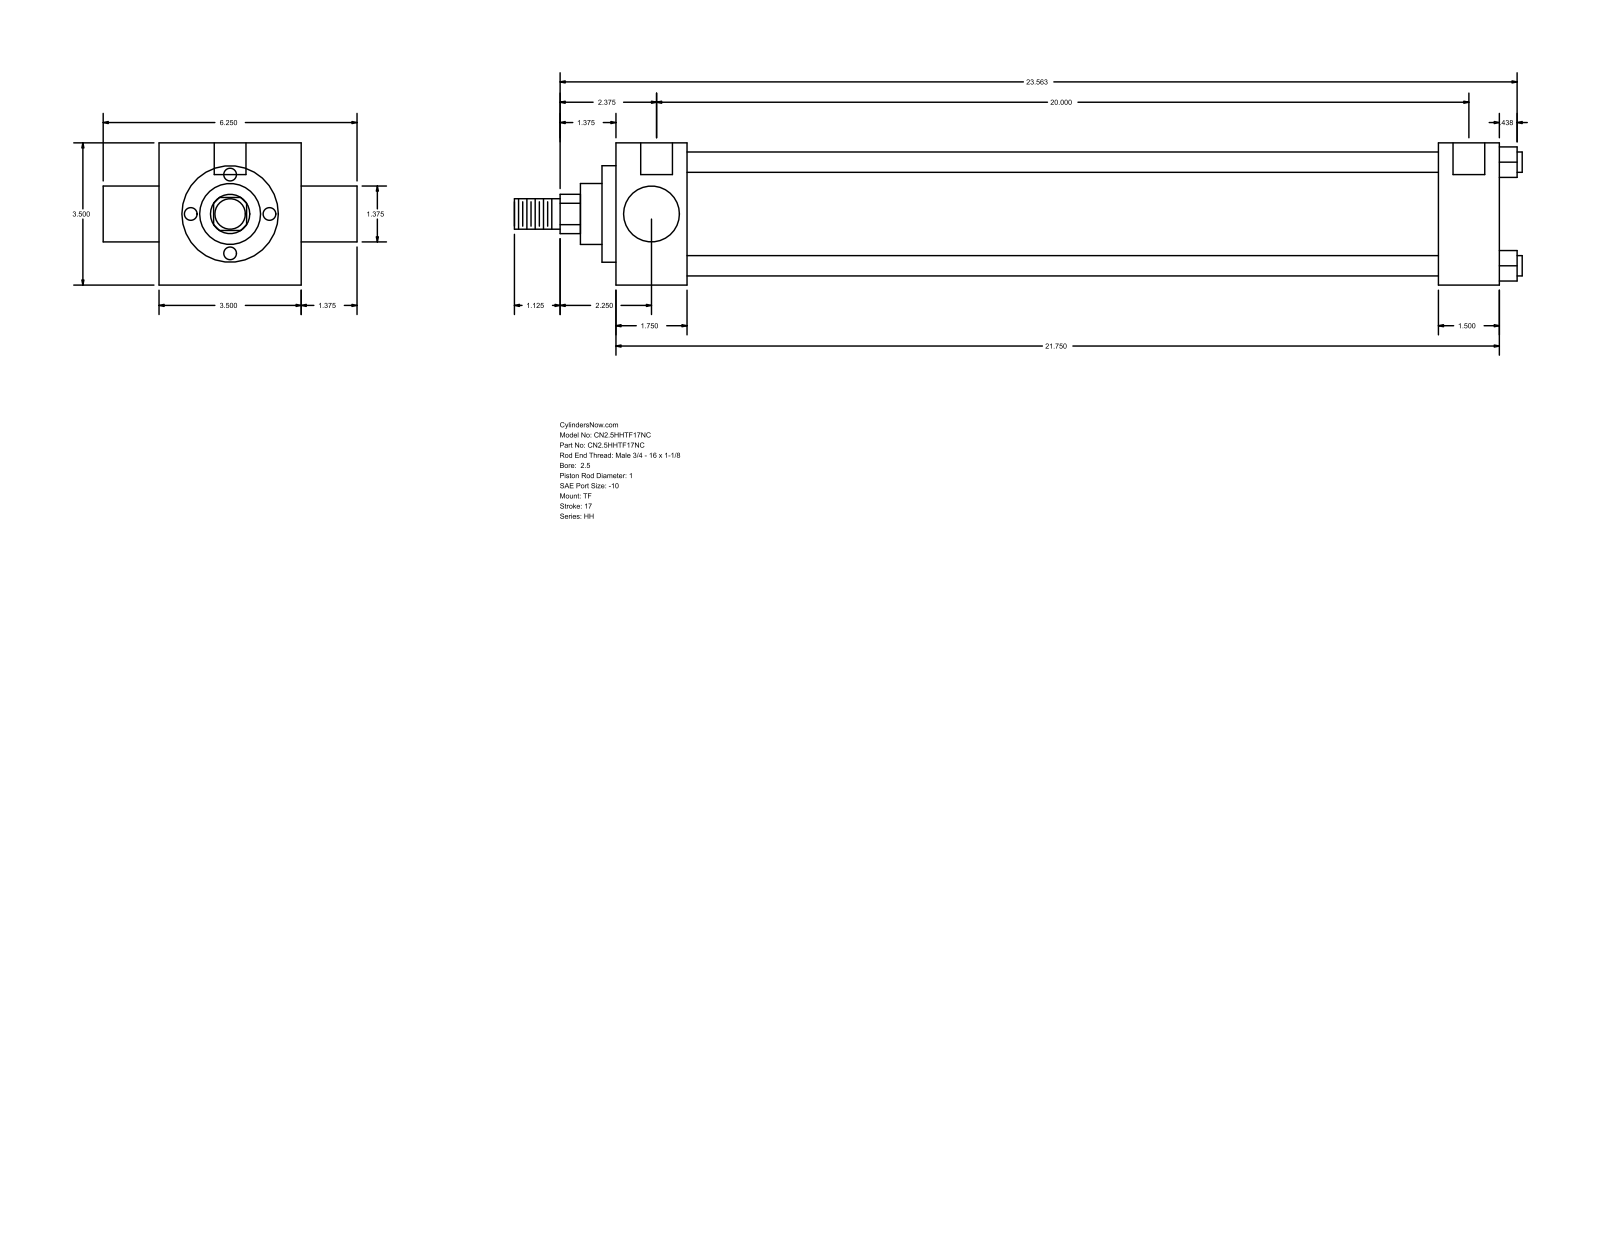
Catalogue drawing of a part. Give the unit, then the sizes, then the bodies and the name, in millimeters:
Units: millimetres
Overall size (bounding box): 630.24 × 158.75 × 88.9
Round holes (diameter × count): ⌀5.56 ×3, ⌀19.84 ×2
Round bosses / shafts (diameter × count): ⌀12.7 ×4, ⌀73.03 ×1, ⌀60.33 ×1, ⌀38.1 ×1, ⌀34.92 ×1, ⌀25.4 ×1, ⌀19.05 ×1
Partial cylindrical surfaces — rounded edges, fillets, slot ends (radius × count): R12.29 ×1
Main face-to-face distances: 88.9, 552.46, 44.46, 508, 514.35, 469.89, 38.11, 34.93, 123.83, 8.73
Hole centre spacings: 1.58, 1.59, 508, 509.58, 509.59, 511.17
Bodies: 0 solids, 86 faces (61 planar, 25 cylindrical, 0 other)
Part name (STEP PRODUCT): HH_TF__0250_1
STEP written by: GSSL Pune (CONFIG_CONTROL_DESIGN)
